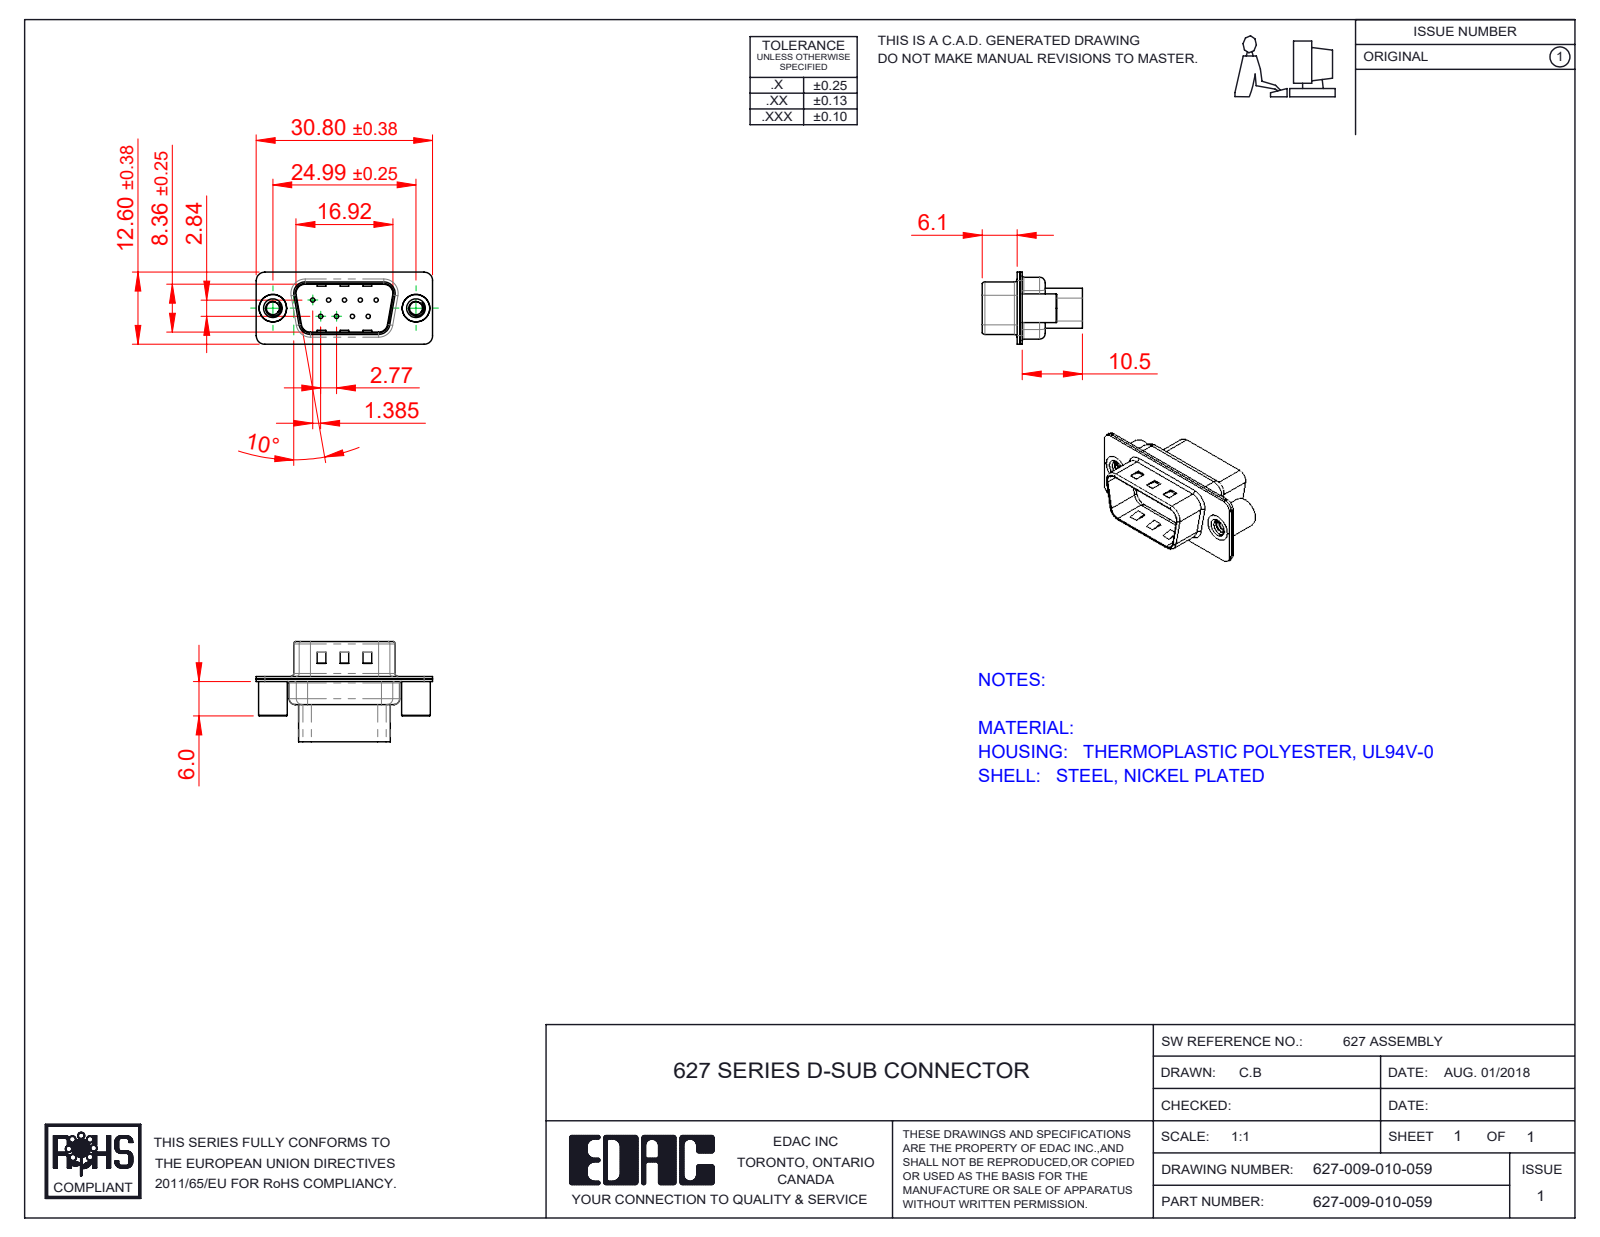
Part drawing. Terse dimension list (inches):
name: 627-009-010-059; 627 Shell Rear_09 Contacts; 627 Housing_09 HP; 627 4-40 Threaded Standoff BS (+1 more)
written by: SolidWorks 2020 (CONFIG_CONTROL_DESIGN)
unit: in
bodies: 5 solids, 398 faces (125 planar, 203 cylindrical, 70 other)
size: 1.213 × 0.689 × 0.496
volume: 0.108 in³; area: 5.83 in²
holes: 9× ⌀0.03, 9× ⌀0.063, 9× ⌀0.079, 2× ⌀0.089, 2× ⌀0.157, 2× ⌀0.189
bosses: 2× ⌀0.197, 2× ⌀0.193
rounds: 18× R0.059, 12× R0.079, 8× R0.02, 8× R0.063, 4× R0.01, 4× R0.024, 4× R0.026, 4× R0.035
face distances: 0.018, 0.016, 0.035, 0.032, 0.377, 0.055, 0.027, 0.302, 0.043, 0.318
hole spacings: 0.124, 0.109, 0.218, 0.198, 0.198, 0.327, 0.294, 0.295
